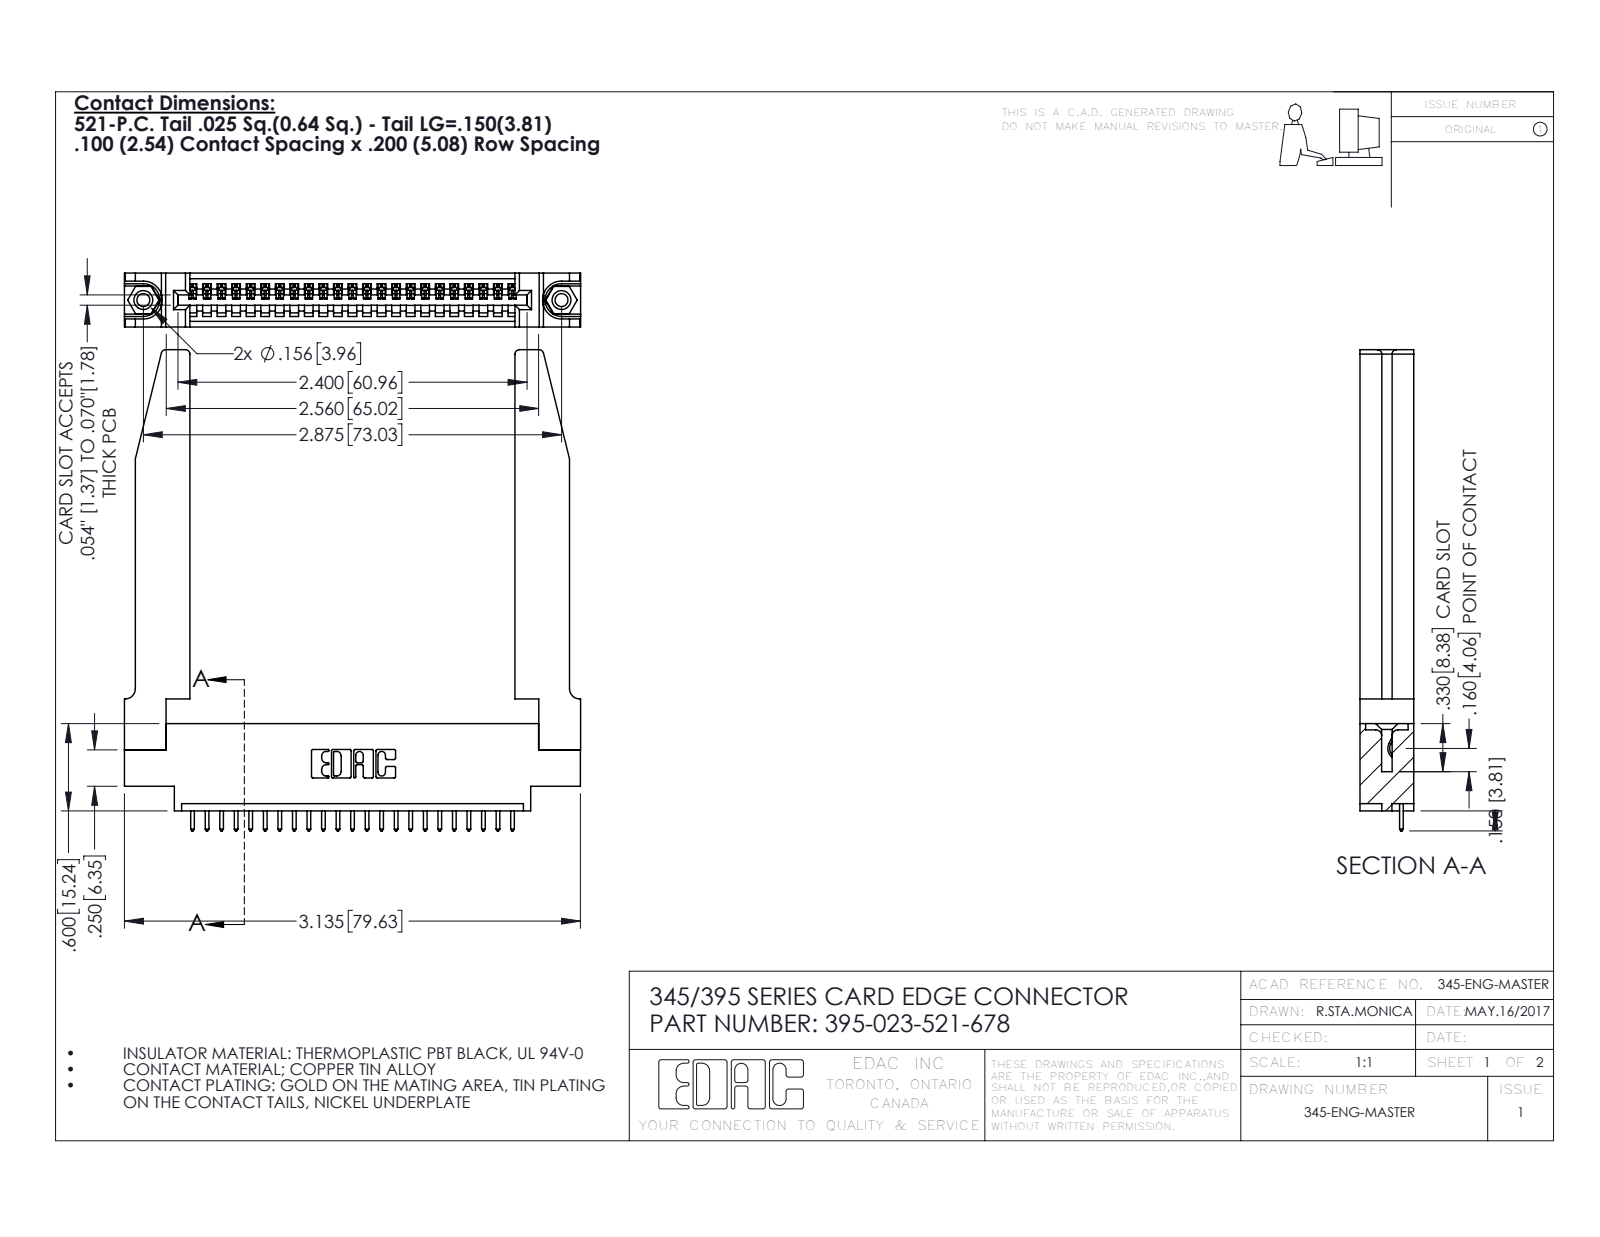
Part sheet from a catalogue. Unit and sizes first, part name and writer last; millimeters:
Units: millimetres
Overall size (bounding box): 84 × 79.7 × 9.4
Round holes (diameter × count): ⌀2.3 ×2, ⌀3.2 ×2, ⌀4 ×2, ⌀1.6 ×1
Round bosses / shafts (diameter × count): ⌀3.9 ×2
Partial cylindrical surfaces — rounded edges, fillets, slot ends (radius × count): R0.2 ×46, R0.3 ×46, R0.3 ×22, R0.8 ×8, R0.2 ×6, R0.8 ×6, R0.7 ×3, R0.8 ×2
Main face-to-face distances: 9.4, 1.8, 7.6, 2.5, 6.9, 0.6, 5.1, 3.8, 3.8, 3.1
Hole centre spacings: 6.9, 67.1, 73
Volume: 15 000 mm³ · Surface area: 16 060 mm²
Bodies: 28 solids, 1698 faces (1146 planar, 500 cylindrical, 52 other)
Part name (STEP PRODUCT): 395-023-521-678; 345-292-001_345-293-121; 345-220-078_345-220-078; 345-250-001_345-250-001-102 (+1 more)
STEP written by: SolidWorks 2016 (CONFIG_CONTROL_DESIGN)
